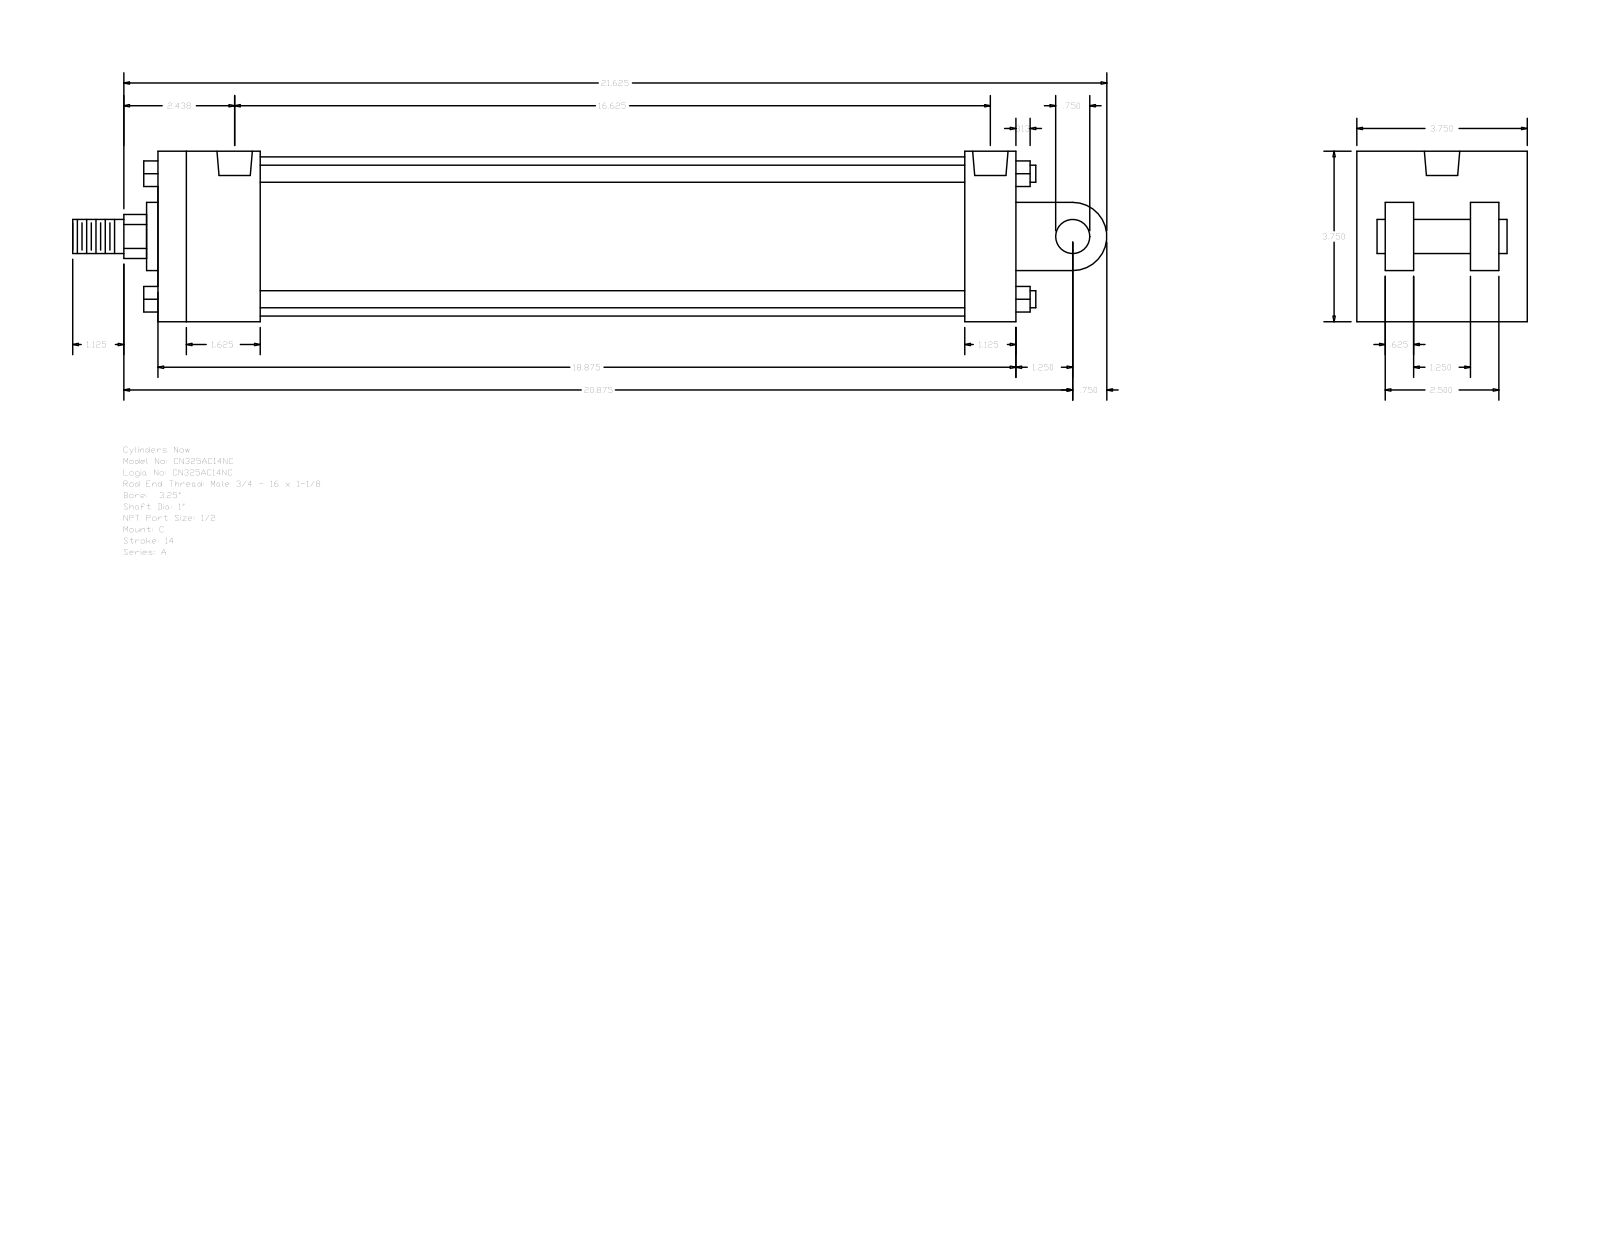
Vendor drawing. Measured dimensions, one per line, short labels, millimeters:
name: A_C__0325_1
written by: GSSL Pune (CONFIG_CONTROL_DESIGN)
unit: mm
bodies: 0 solids, 135 faces (102 planar, 33 cylindrical, 0 other)
size: 577.85 × 95.25 × 95.25
holes: 4× ⌀8.73, 2× ⌀19.77
bosses: 4× ⌀9.53, 2× ⌀19.05, 1× ⌀88.9, 1× ⌀38.1, 1× ⌀25.4
rounds: 1× R12.29, 1× R19.05
face distances: 95.24, 479.43, 15.87, 63.5, 79.37, 31.74, 47.63, 66.67, 450.85, 28.58
hole spacings: 3.18, 415.92, 419.1, 422.28
